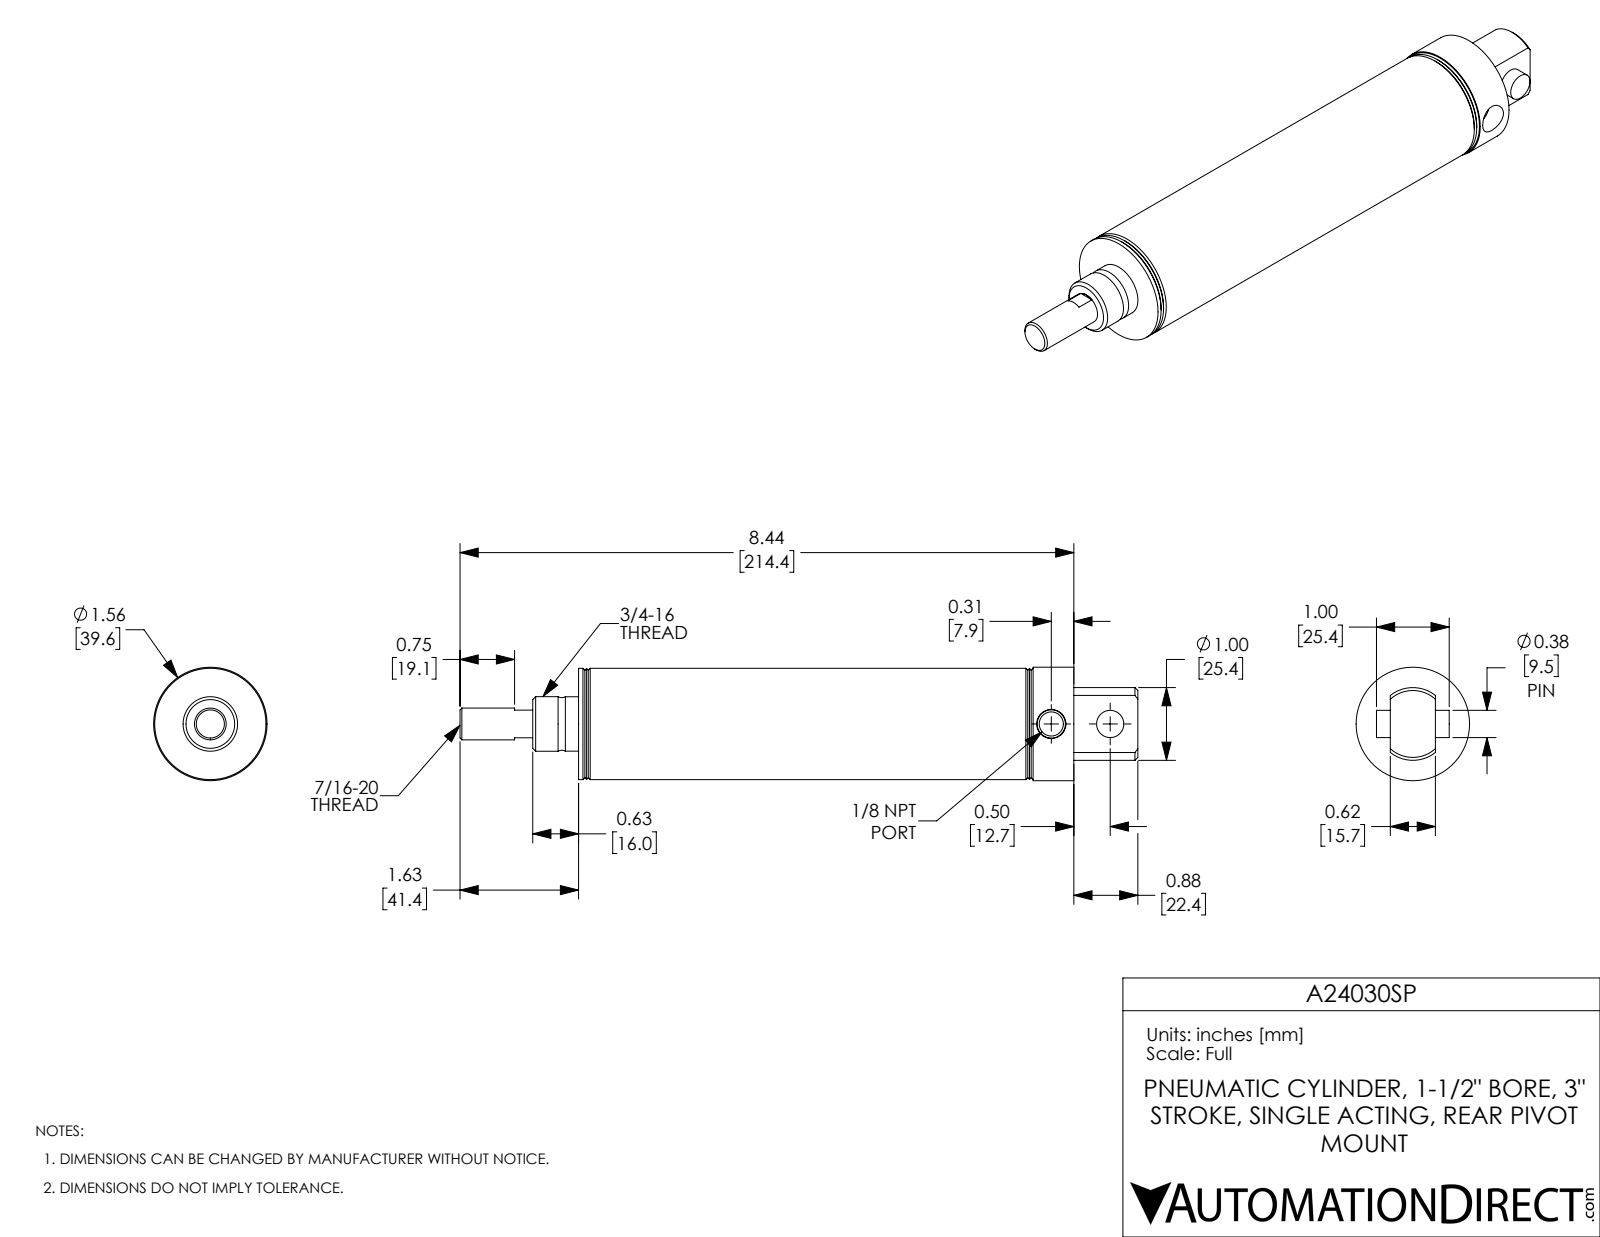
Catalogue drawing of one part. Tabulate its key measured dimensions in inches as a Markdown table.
| quantity | value |
| --- | --- |
| part name | A24030SP-MainBody; A24030SP-Rod; A24030SP-PIN; A24030SP |
| STEP written by | SolidWorks 2017 (AUTOMOTIVE_DESIGN) |
| units | inches |
| bodies | 3 solids, 78 faces (22 planar, 26 cylindrical, 30 other) |
| overall size | 9.32 × 1.56 × 1.56 |
| volume | 8.615 in³ |
| surface area | 80.32 in² |
| round holes (diameter × count) | 0.332 × 1, 0.375 × 1, 0.437 × 1, 1.5 × 1 |
| round bosses / shafts (diameter × count) | 1.56 × 1, 1.53 × 1, 0.75 × 1, 0.747 × 1 |
| partial cylindrical surfaces (radius × count) | 0.5 × 1 |
| main face-to-face distances | 0.5, 3.5, 3, 5, 4.5, 1.5, 1.81, 2.31, 5.31, 6.81 |
| hole center spacings | 0.81 |
